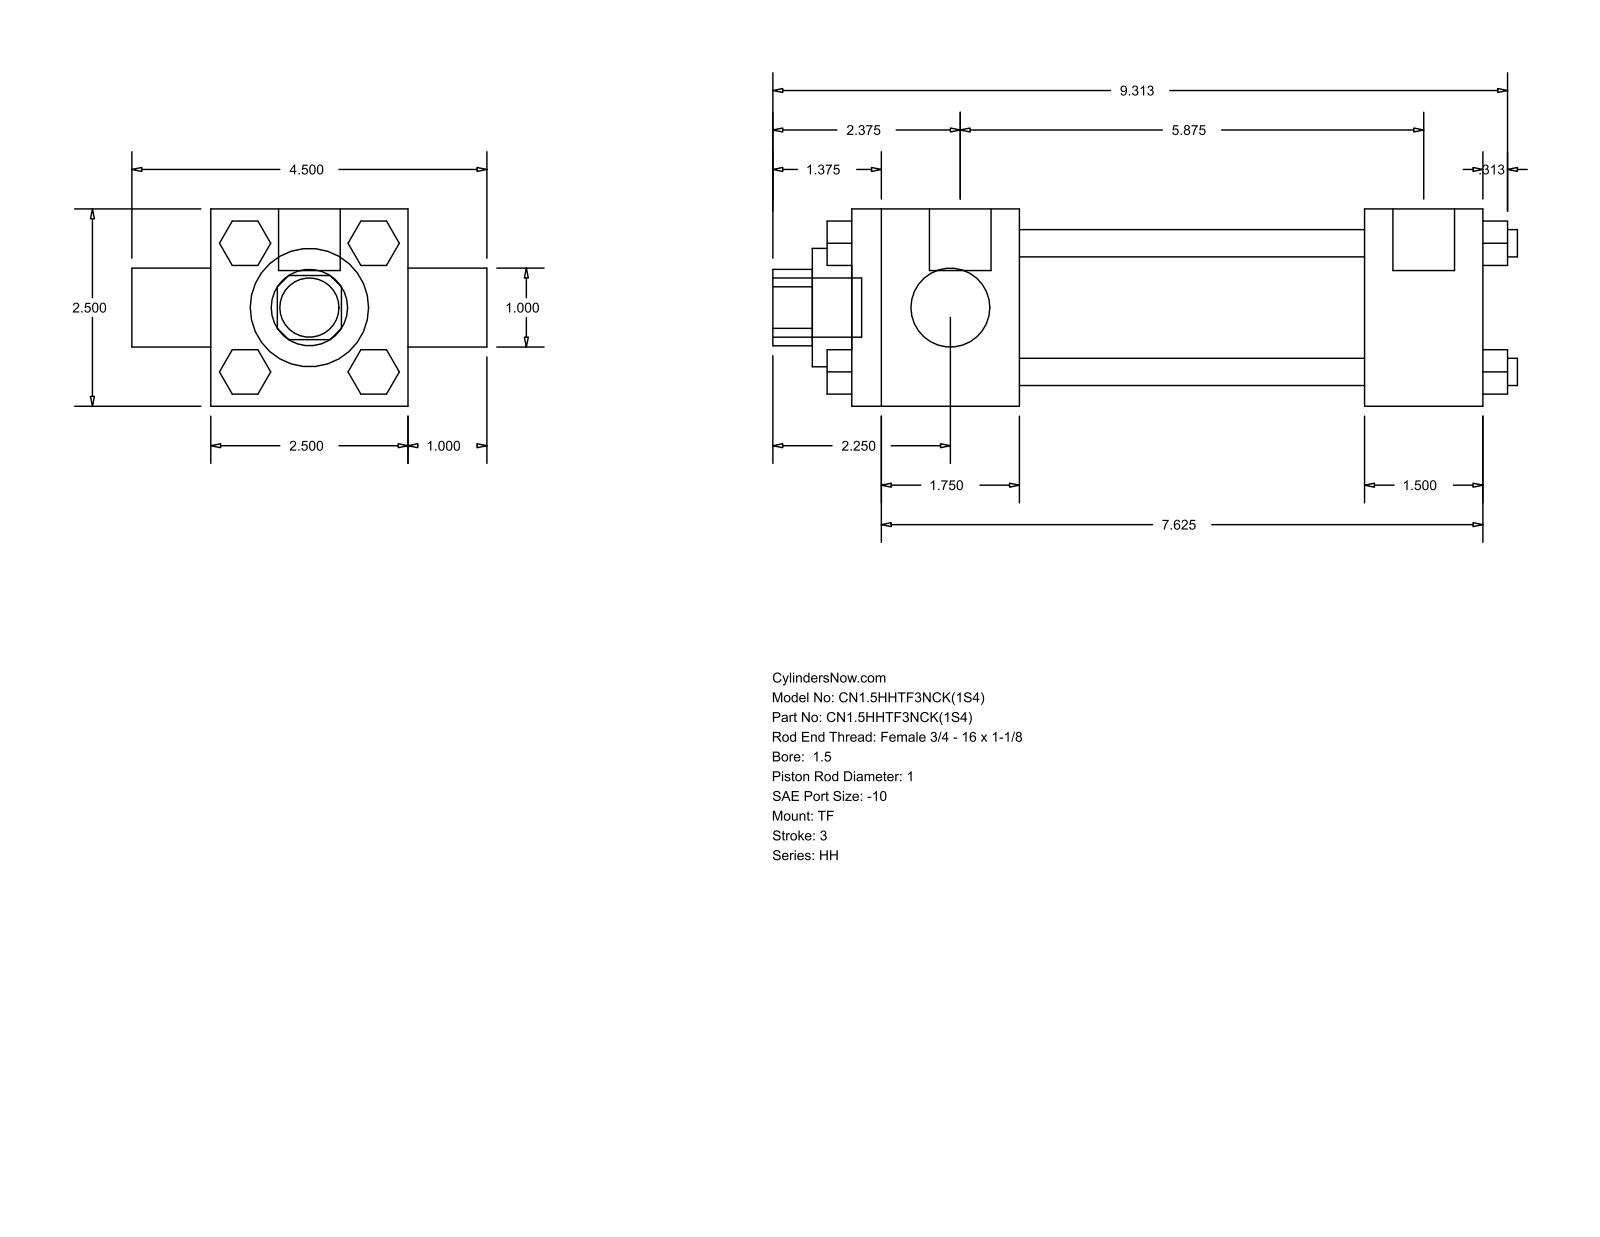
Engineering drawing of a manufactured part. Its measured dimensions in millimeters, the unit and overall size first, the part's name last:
Units: millimetres
Overall size (bounding box): 239.71 × 114.3 × 63.5
Round holes (diameter × count): ⌀25.4 ×2, ⌀38.1 ×1, ⌀44.45 ×1
Round bosses / shafts (diameter × count): ⌀8.76 ×4, ⌀5.56 ×3, ⌀19.84 ×2, ⌀19.05 ×1
Partial cylindrical surfaces — rounded edges, fillets, slot ends (radius × count): R12.29 ×1
Main face-to-face distances: 63.5, 149.22, 111.12, 38.1, 53.98, 165.1, 203.2, 211.14, 25.4, 20.7
Bodies: 0 solids, 120 faces (92 planar, 28 cylindrical, 0 other)
Part name (STEP PRODUCT): HH_TF__0150_1
STEP written by: GSSL Pune (CONFIG_CONTROL_DESIGN)
